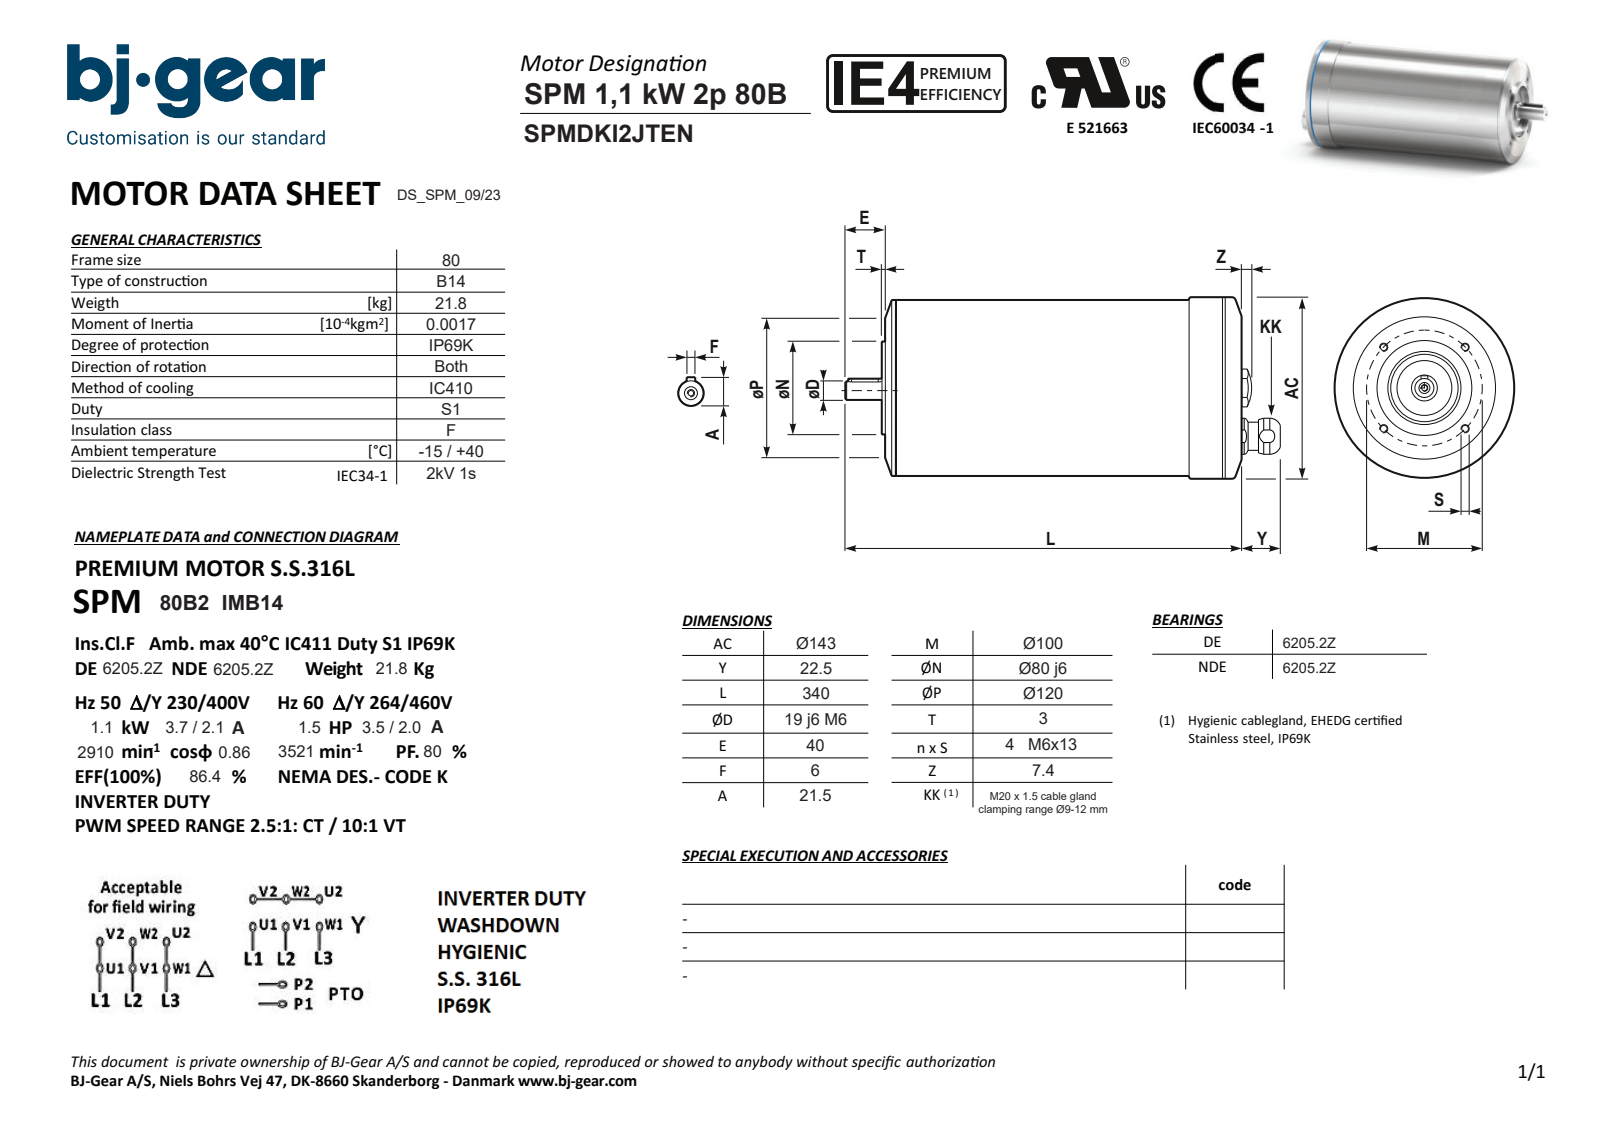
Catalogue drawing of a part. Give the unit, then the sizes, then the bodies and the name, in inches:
Units: inches
Overall size (bounding box): 14.469 × 5.63 × 5.63
Round holes (diameter × count): ⌀0.194 ×5, ⌀0.252 ×1, ⌀0.276 ×1, ⌀0.528 ×1, ⌀2.677 ×1
Round bosses / shafts (diameter × count): ⌀5.63 ×1, ⌀5.629 ×1, ⌀5.472 ×1, ⌀5.472 ×1, ⌀3.15 ×1, ⌀0.984 ×1, ⌀0.787 ×1, ⌀0.748 ×1
Partial cylindrical surfaces — rounded edges, fillets, slot ends (radius × count): R0.118 ×2, R0.504 ×1
Main face-to-face distances: 11.811, 0.236, 11.575, 0.354, 11.929, 0.118, 0.945, 13.386, 1.811, 1.575
Hole centre spacings: 1.969, 2.784, 1.396, 3.206, 3.937, 1.496
Volume: 278.9 in³ · Surface area: 261.1 in²
Bodies: 1 solid, 87 faces (30 planar, 32 cylindrical, 25 other)
Part name (STEP PRODUCT): SPMDKI2JTENN4KSA1-N---NNN
STEP written by: Solid Edge (AUTOMOTIVE_DESIGN)
